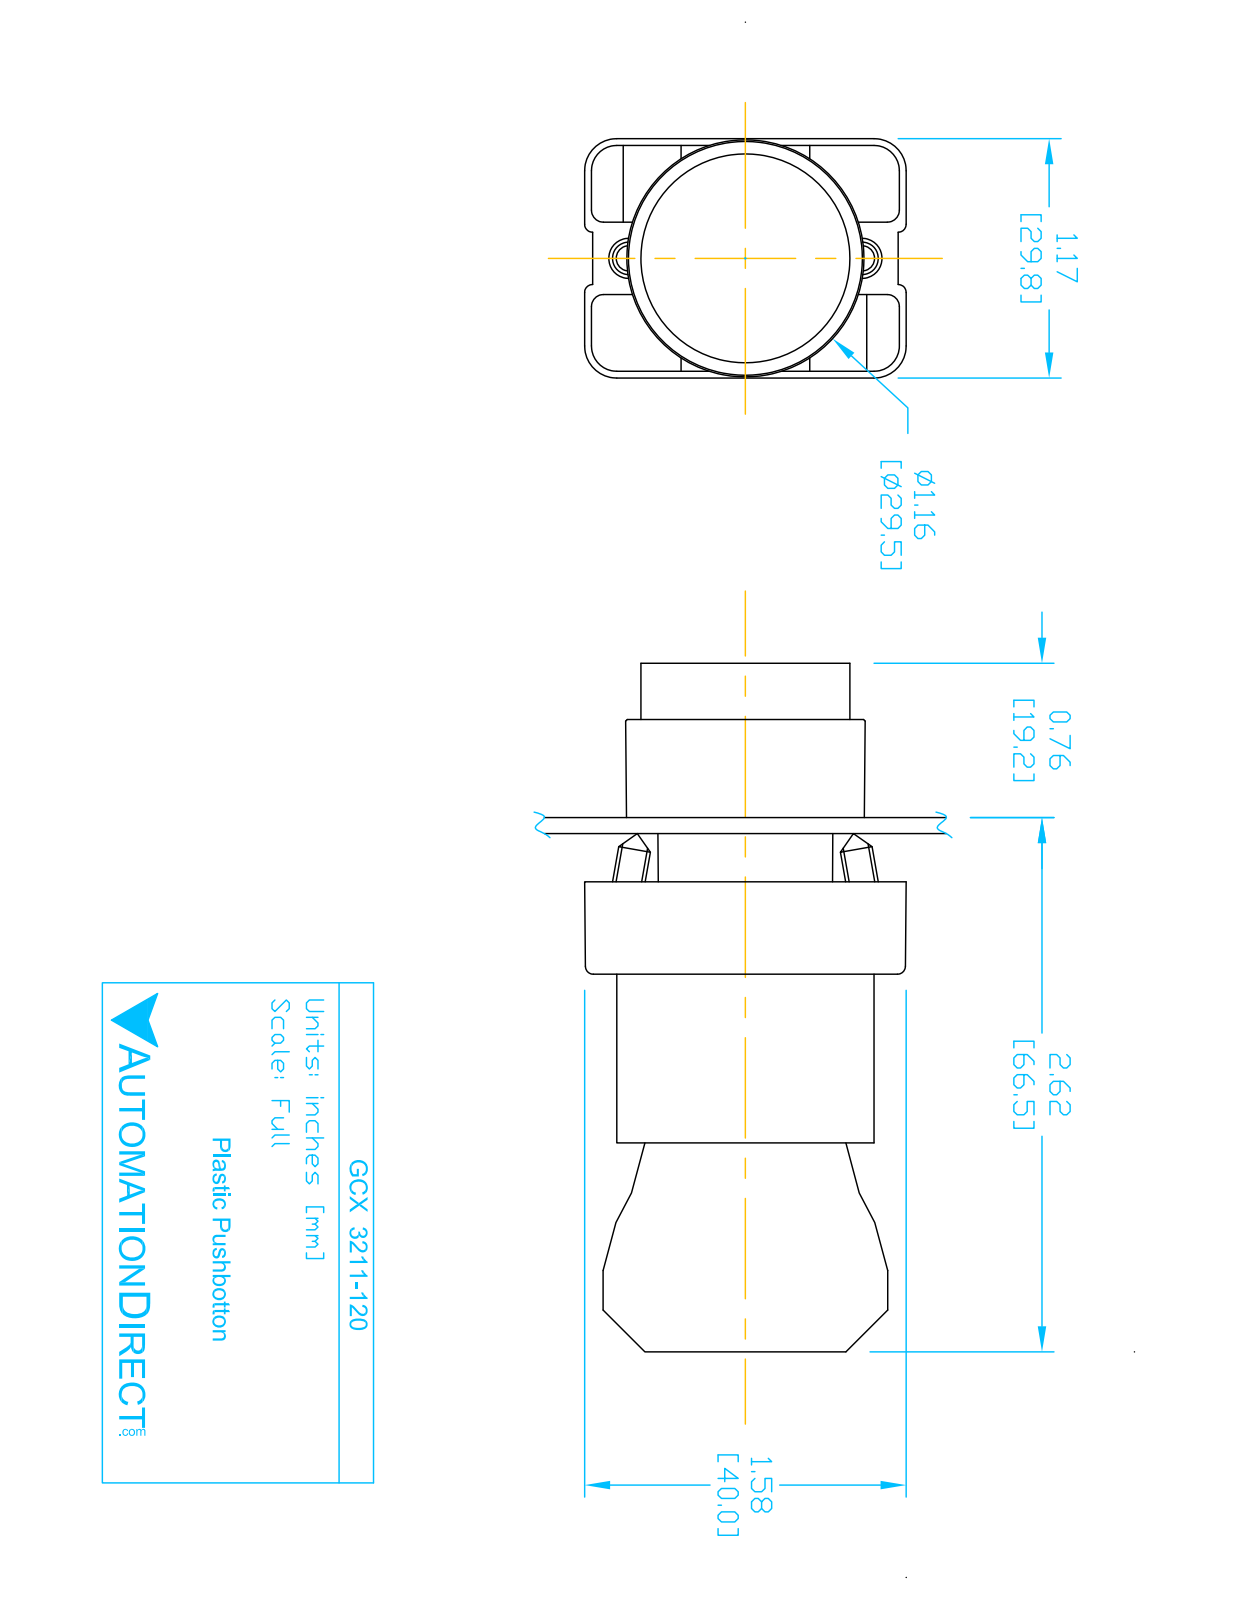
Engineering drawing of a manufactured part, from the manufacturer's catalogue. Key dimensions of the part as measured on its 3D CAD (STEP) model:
Part name (STEP PRODUCT): GCX3211-120; ECX1050; ecx1030; GCX3211 OPERATOR (+1 more)
STEP written by: SolidWorks 2016 (AUTOMOTIVE_DESIGN)
Units: inches
Bodies: 7 solids, 425 faces (250 planar, 144 cylindrical, 31 other)
Overall size (bounding box): 3.319 × 1.581 × 1.177
Volume: 2.721 in³ · Surface area: 36.32 in²
Round holes (diameter × count): ⌀0.079 ×2, ⌀0.124 ×2, ⌀0.13 ×2, ⌀0.087 ×1, ⌀0.197 ×1, ⌀0.469 ×1, ⌀0.878 ×1, ⌀0.888 ×1, ⌀1.024 ×1
Round bosses / shafts (diameter × count): ⌀0.157 ×4, ⌀1.175 ×1, ⌀1.004 ×1, ⌀0.945 ×1, ⌀0.856 ×1, ⌀0.78 ×1, ⌀0.504 ×1
Partial cylindrical surfaces — rounded edges, fillets, slot ends (radius × count): R0.059 ×24, R0.041 ×12, R0.124 ×12, R0.157 ×12, R0.039 ×8, R0.128 ×2, R0.02 ×1, R0.063 ×1
Main face-to-face distances: 0.827, 0.579, 1.171, 2.02, 1.193, 0.031, 0.033, 0.573, 1.165, 0.593
Hole centre spacings: 0.236, 0.544, 0.472, 0.49
